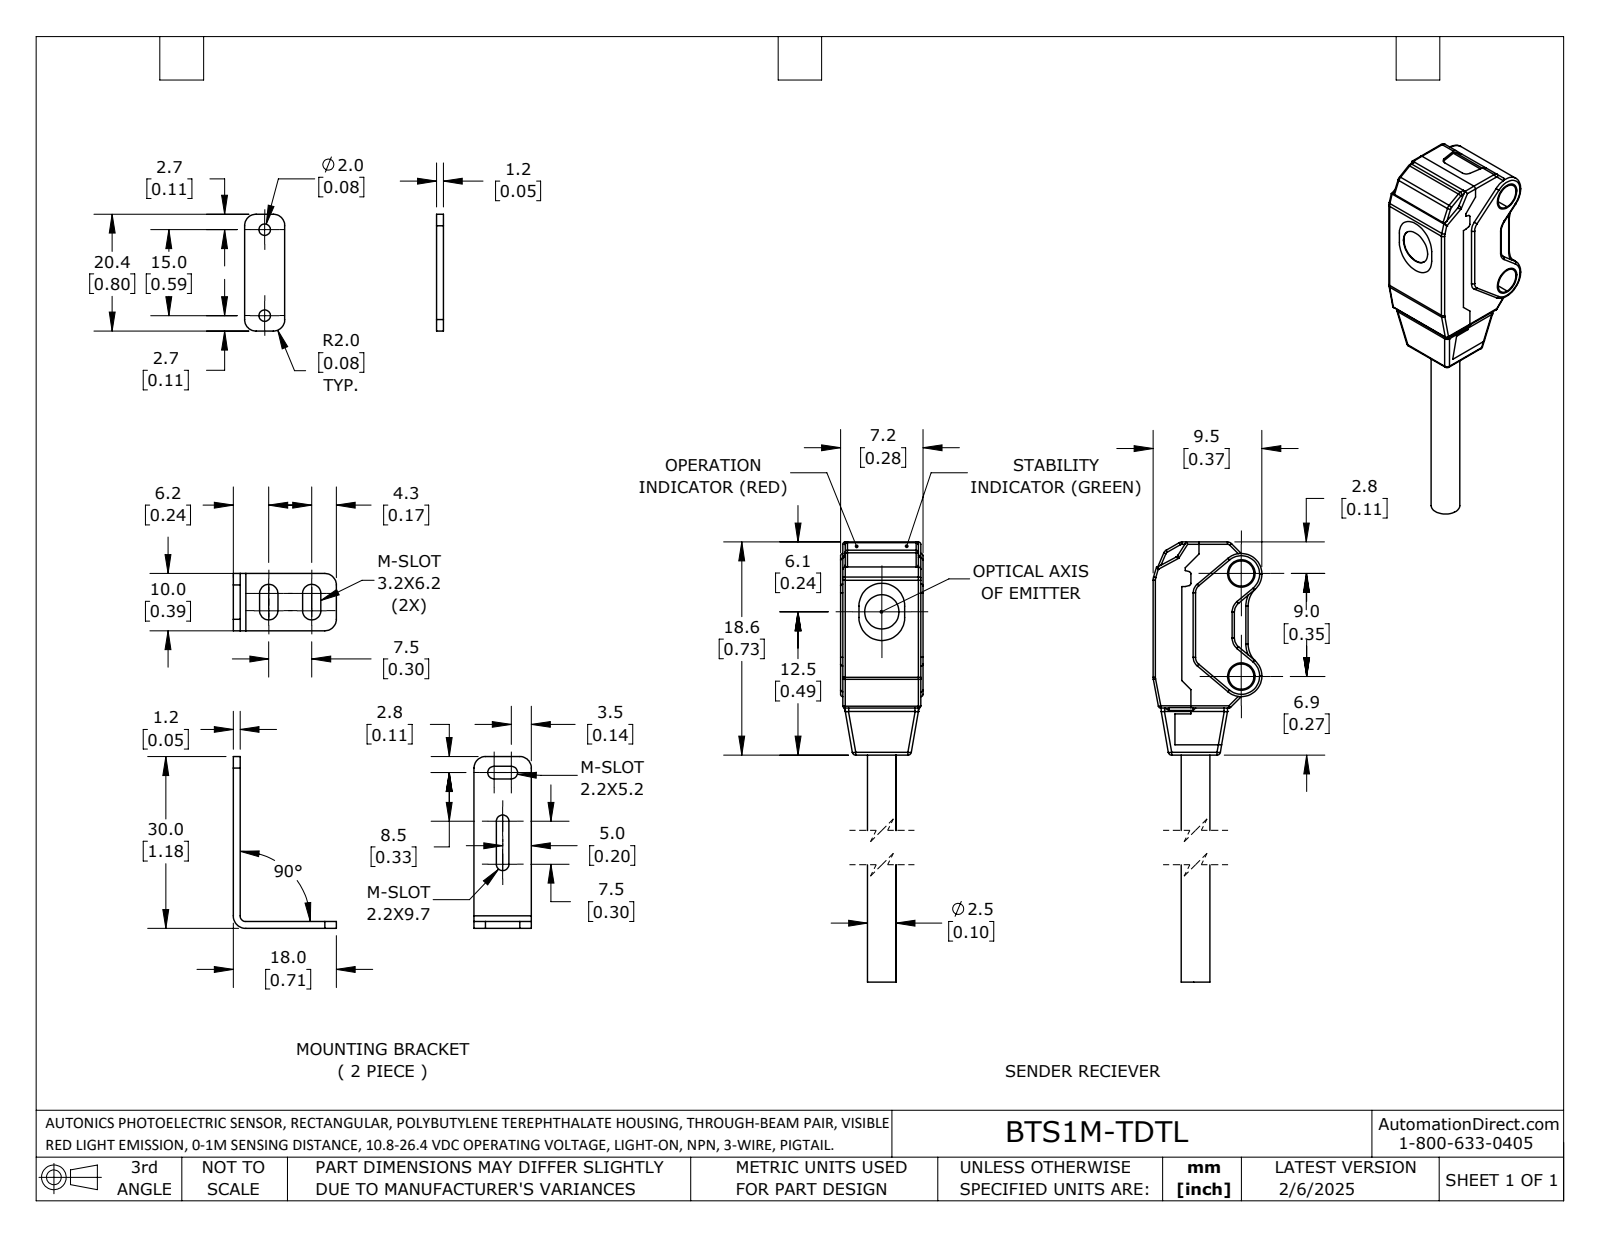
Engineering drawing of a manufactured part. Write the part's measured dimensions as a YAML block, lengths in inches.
part_name: "BTS1M-TDTL_BTS1M-TDTL-P_BTS1M-TDTD_BTS1M-TDTD-P_RECIEVER; BTS1M-TDTL_BTS1M-TDTL-P_BTS1M-TDTD_BTS1M-TDTD-P_SENDER; BTS1M-TDTL_BTS1M-TDTL-P_BTS1M-TDTD_BTS1M-TDTD-P"
step_written_by: "SolidWorks 2024 (AUTOMOTIVE_DESIGN)"
units: inches
bodies: {solids: 10, faces: 1072, planar: 654, cylindrical: 274, other: 144}
overall_size: [3, 1.404, 1.134]
volume: 0.204
surface_area: 7.171
round_holes:
  - {diameter: 0.079, count: 5}
  - {diameter: 0.087, count: 4}
  - {diameter: 0.118, count: 1}
round_bosses_or_shafts:
  - {diameter: 0.157, count: 4}
  - {diameter: 0.098, count: 2}
partial_cylinders:
  - {radius: 0.008, count: 76}
  - {radius: 0.012, count: 22}
  - {radius: 0.079, count: 20}
  - {radius: 0.02, count: 12}
  - {radius: 0.007, count: 8}
  - {radius: 0.043, count: 8}
  - {radius: 0.063, count: 8}
  - {radius: 0.017, count: 6}
face_to_face_distances: [0.047, 0.331, 0.276, 0.323, 0.055, 0.283, 0.378, 2.606, 0.268, 0.106]
hole_center_spacings: [0.354, 2.606, 2.63]
